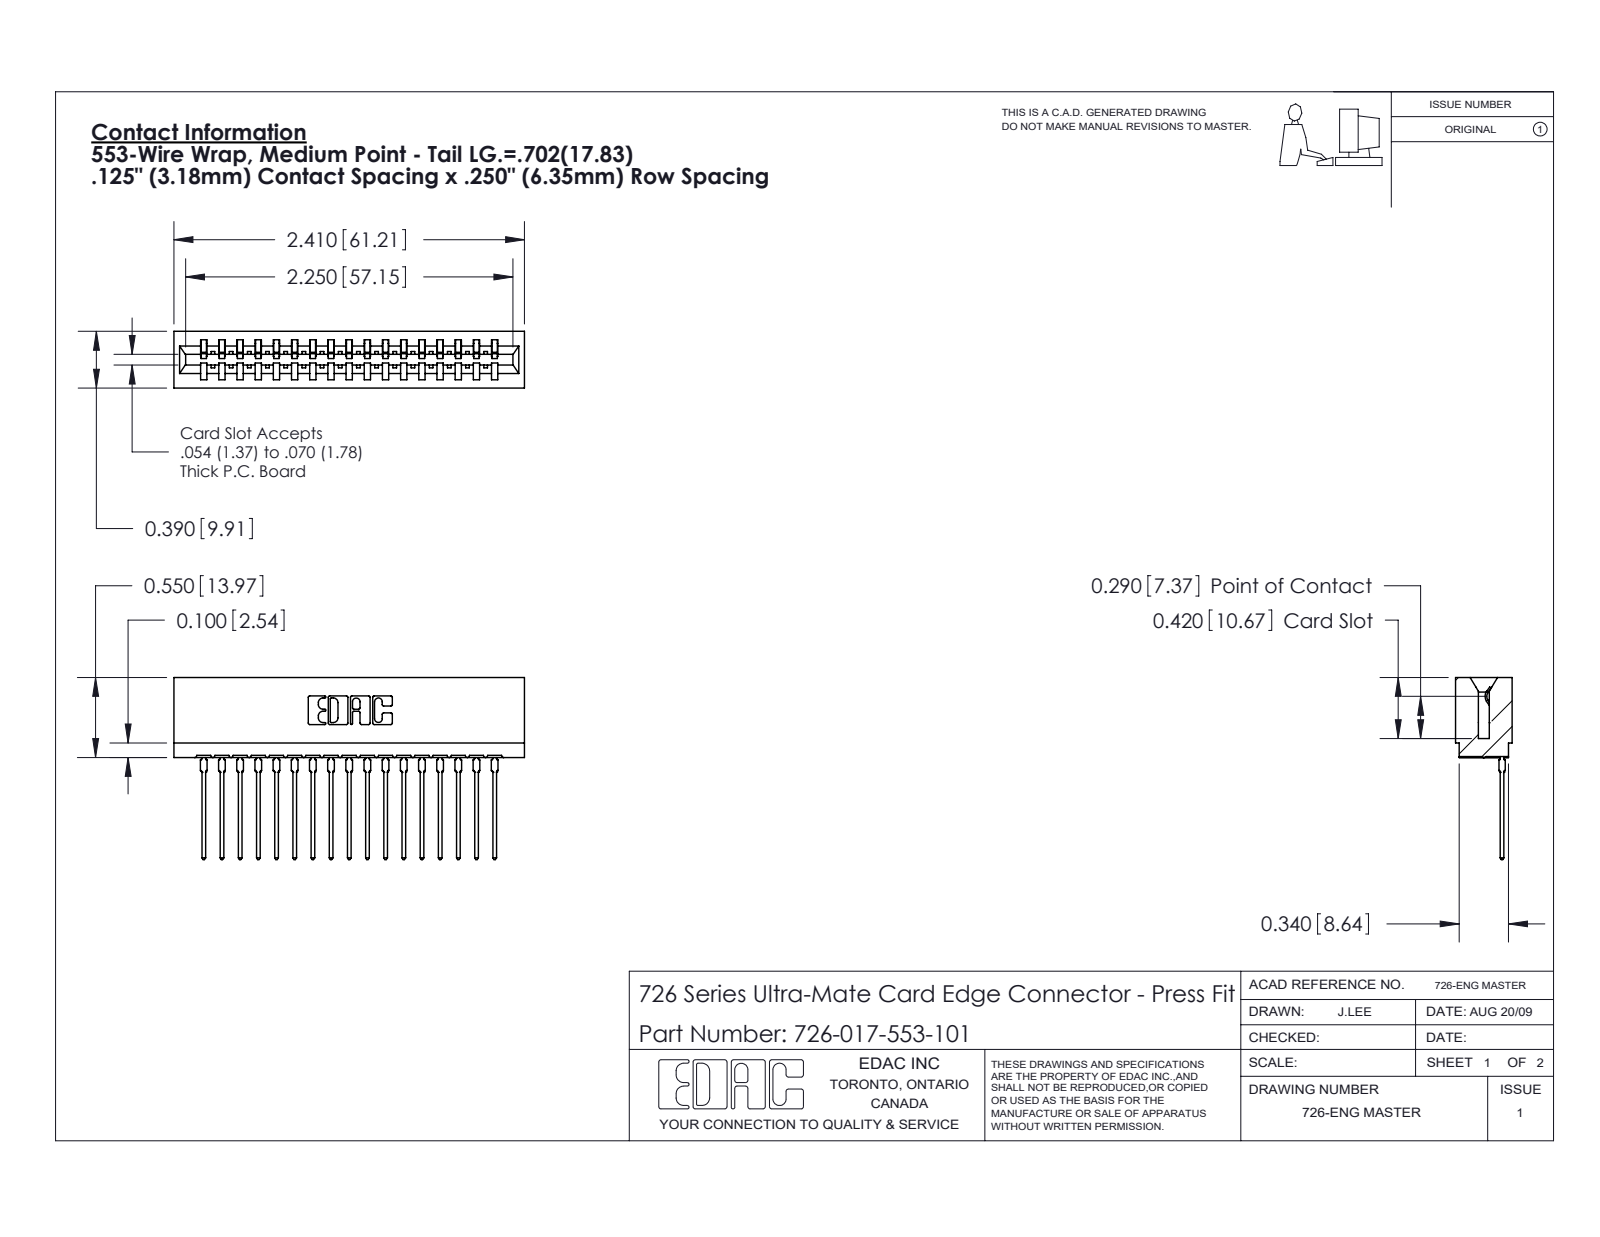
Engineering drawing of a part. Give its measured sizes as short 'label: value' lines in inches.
name: 726-017-553-101; 726 Part_.515 Slot Depth - 01; 746-292-001_553
written by: SolidWorks 2020 (CONFIG_CONTROL_DESIGN)
unit: in
bodies: 18 solids, 1933 faces (1126 planar, 365 cylindrical, 442 other)
size: 2.41 × 1.251 × 0.39
volume: 0.346 in³; area: 13.34 in²
rounds: 34× R0.021, 22× R0.01, 18× R0.015, 6× R0.007, 6× R0.031, 4× R0.005, 4× R0.011, 3× R0.026
face distances: 0.057, 0.333, 0.25, 0.39, 0.025, 0.307, 0.083, 0.5, 0.75, 0.125
